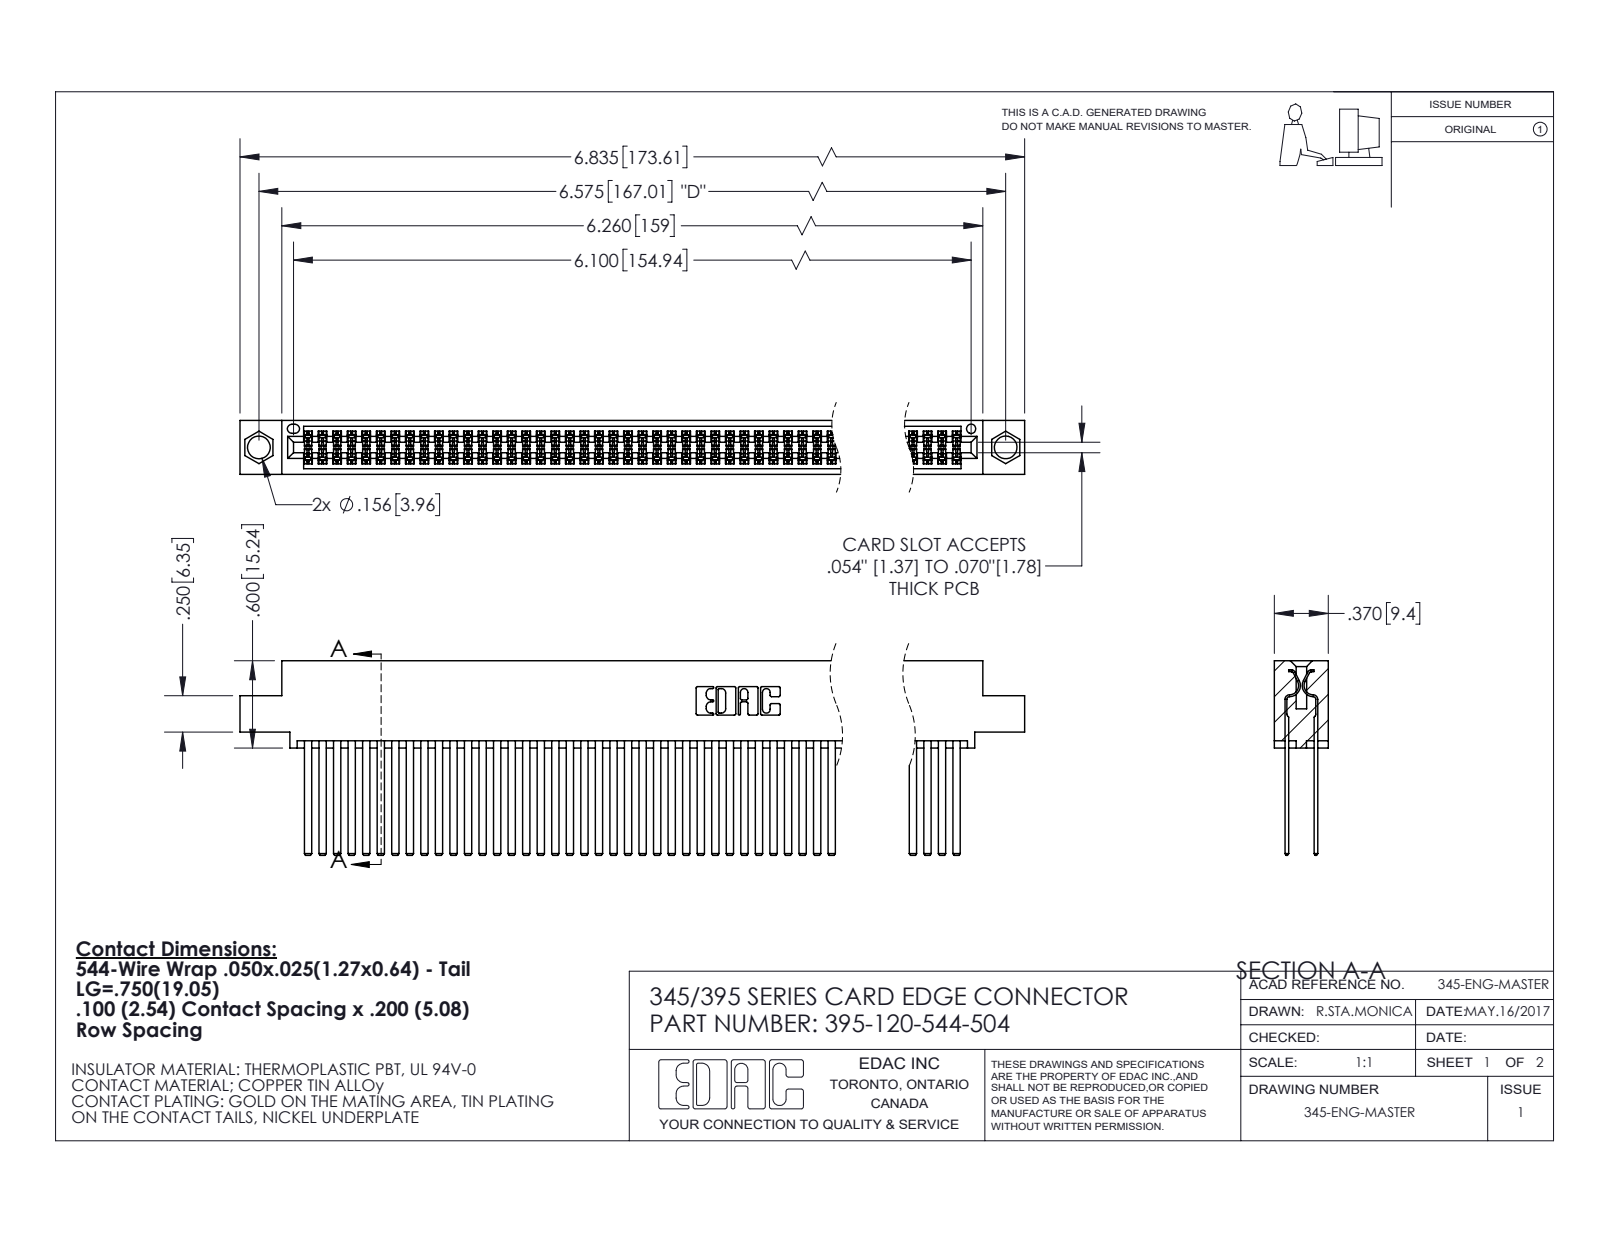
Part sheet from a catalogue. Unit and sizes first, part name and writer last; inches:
Units: inches
Overall size (bounding box): 6.835 × 1.337 × 0.37
Round holes (diameter × count): ⌀0.156 ×2, ⌀0.064 ×1
Partial cylindrical surfaces — rounded edges, fillets, slot ends (radius × count): R0.006 ×180, R0.01 ×22, R0.007 ×6, R0.031 ×6, R0.026 ×3, R0.014 ×2, R0.019 ×2, R0.022 ×2
Main face-to-face distances: 0.2, 0.025, 0.298, 0.072, 0.098, 0.272, 0.225, 0.175, 0.37, 0.05
Hole centre spacings: 0.27, 6.339, 6.575
Volume: 1.131 in³ · Surface area: 50.56 in²
Bodies: 121 solids, 5424 faces (3578 planar, 1846 cylindrical, 0 other)
Part name (STEP PRODUCT): 345 Part_0.110 Offset - 0.156 Dia-TI; 395-120-544-504; 345-292-001_345-293-144
STEP written by: SolidWorks 2020 (CONFIG_CONTROL_DESIGN)
